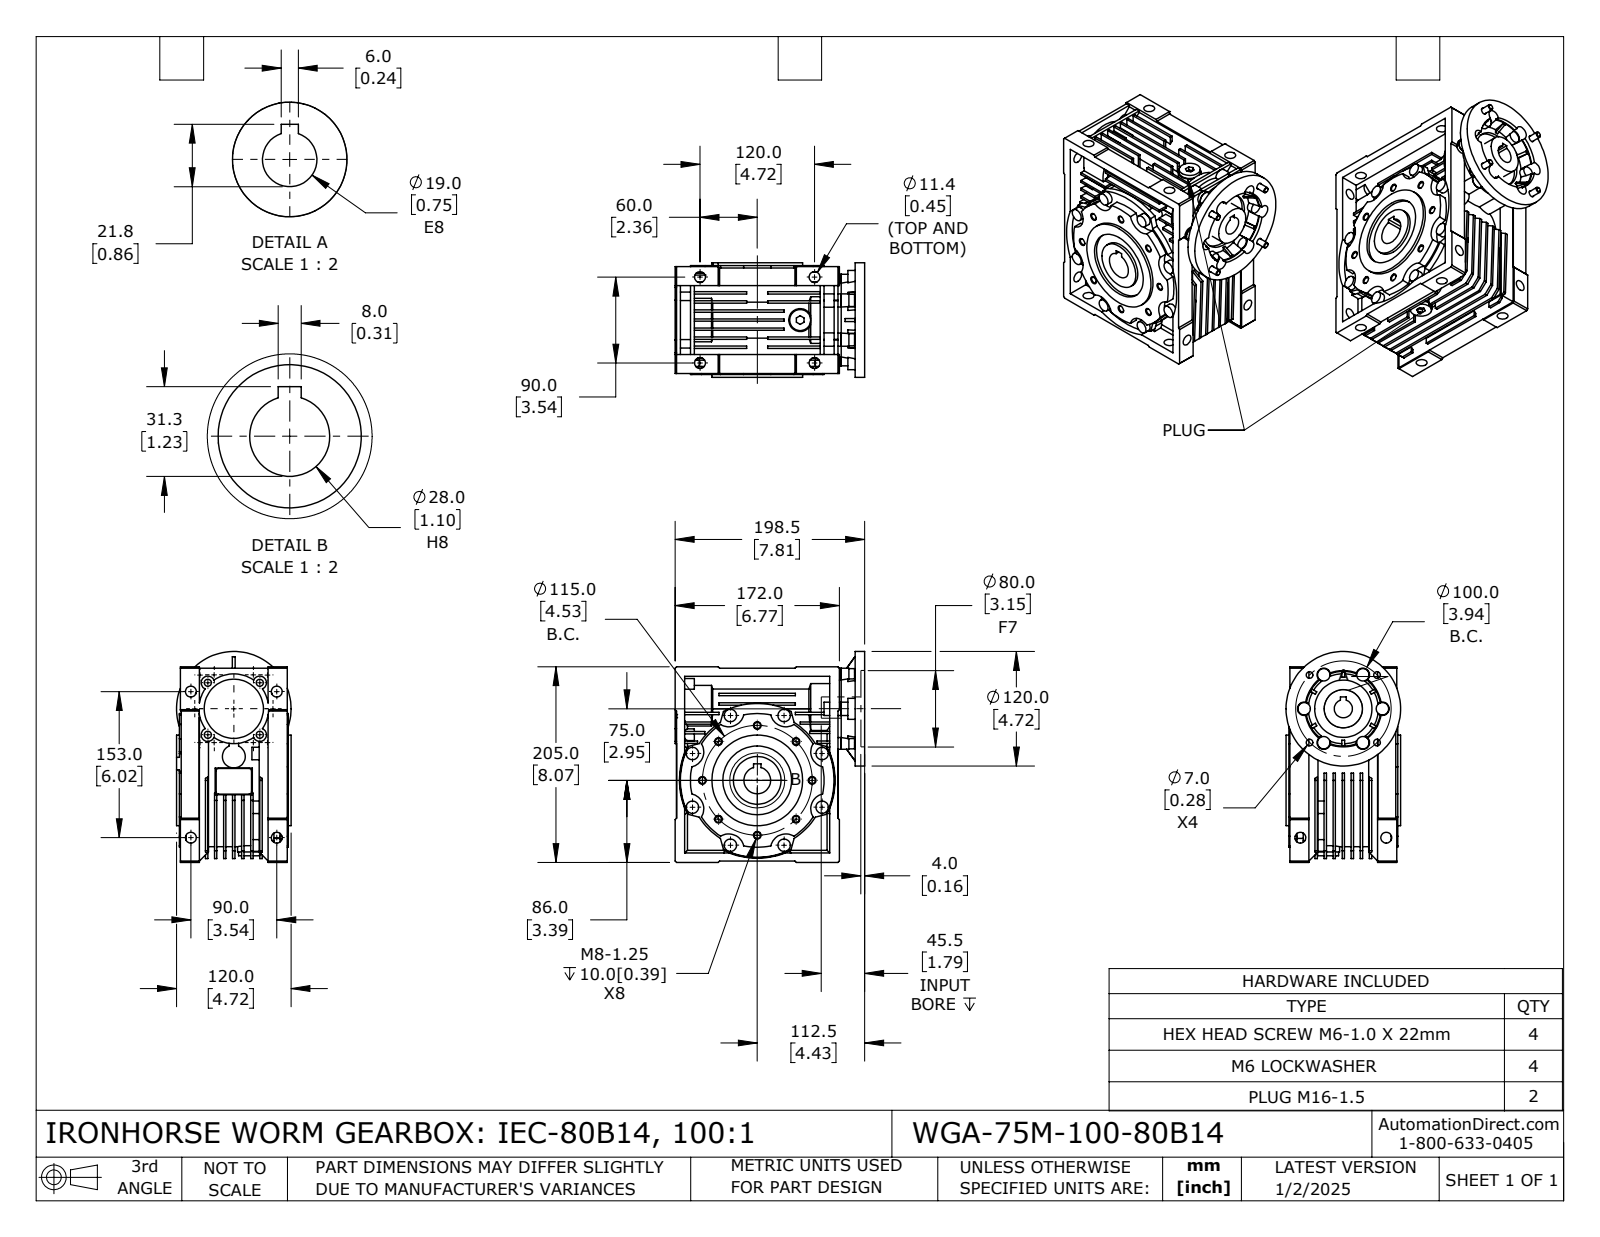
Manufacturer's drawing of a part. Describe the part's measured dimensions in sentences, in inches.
The part is named "WGA-75M-100-80B14". Its 3-D file was written by "SolidWorks 2024 (CONFIG_CONTROL_DESIGN)". It is 16 solids with 1304 faces: 703 planar, 433 cylindrical and 168 other. Overall it measures 8.701 by 8.228 by 4.724 inches. Its volume is 174.1 cubic inches and its surface area 745.4 square inches. Round holes: 8 of diameter 0.262, 8 of diameter 0.448, 4 of diameter 0.24, 4 of diameter 0.276, 4 of diameter 0.293, 2 of diameter 0.571, 1 of diameter 0.748, 1 of diameter 0.787, 1 of diameter 1.102, 1 of diameter 1.535, 1 of diameter 1.654, 1 of diameter 1.969. Round bosses or shafts: 14 of diameter 0.512, 4 of diameter 0.48, 4 of diameter 0.236, 3 of diameter 0.945, 2 of diameter 0.866, 2 of diameter 0.622, 2 of diameter 0.539, 1 of diameter 5.509. Partial cylindrical surfaces (rounded edges, fillets, slot ends): 10 of radius 0.276, 8 of radius 0.63, 6 of radius 0.433, 4 of radius 0.098, 1 of radius 1.417, 1 of radius 1.437, 1 of radius 1.535, 1 of radius 1.575. The main face-to-face distances are 0.374, 0.098, 0.748, 0.472, 0.394, 0.276, 0.65, 1.122, 1.093, 0.846. The hole center spacings are 1.733, 2.264, 2.485, 3.202, 4.183, 0.453, 1.515, 1.969.
